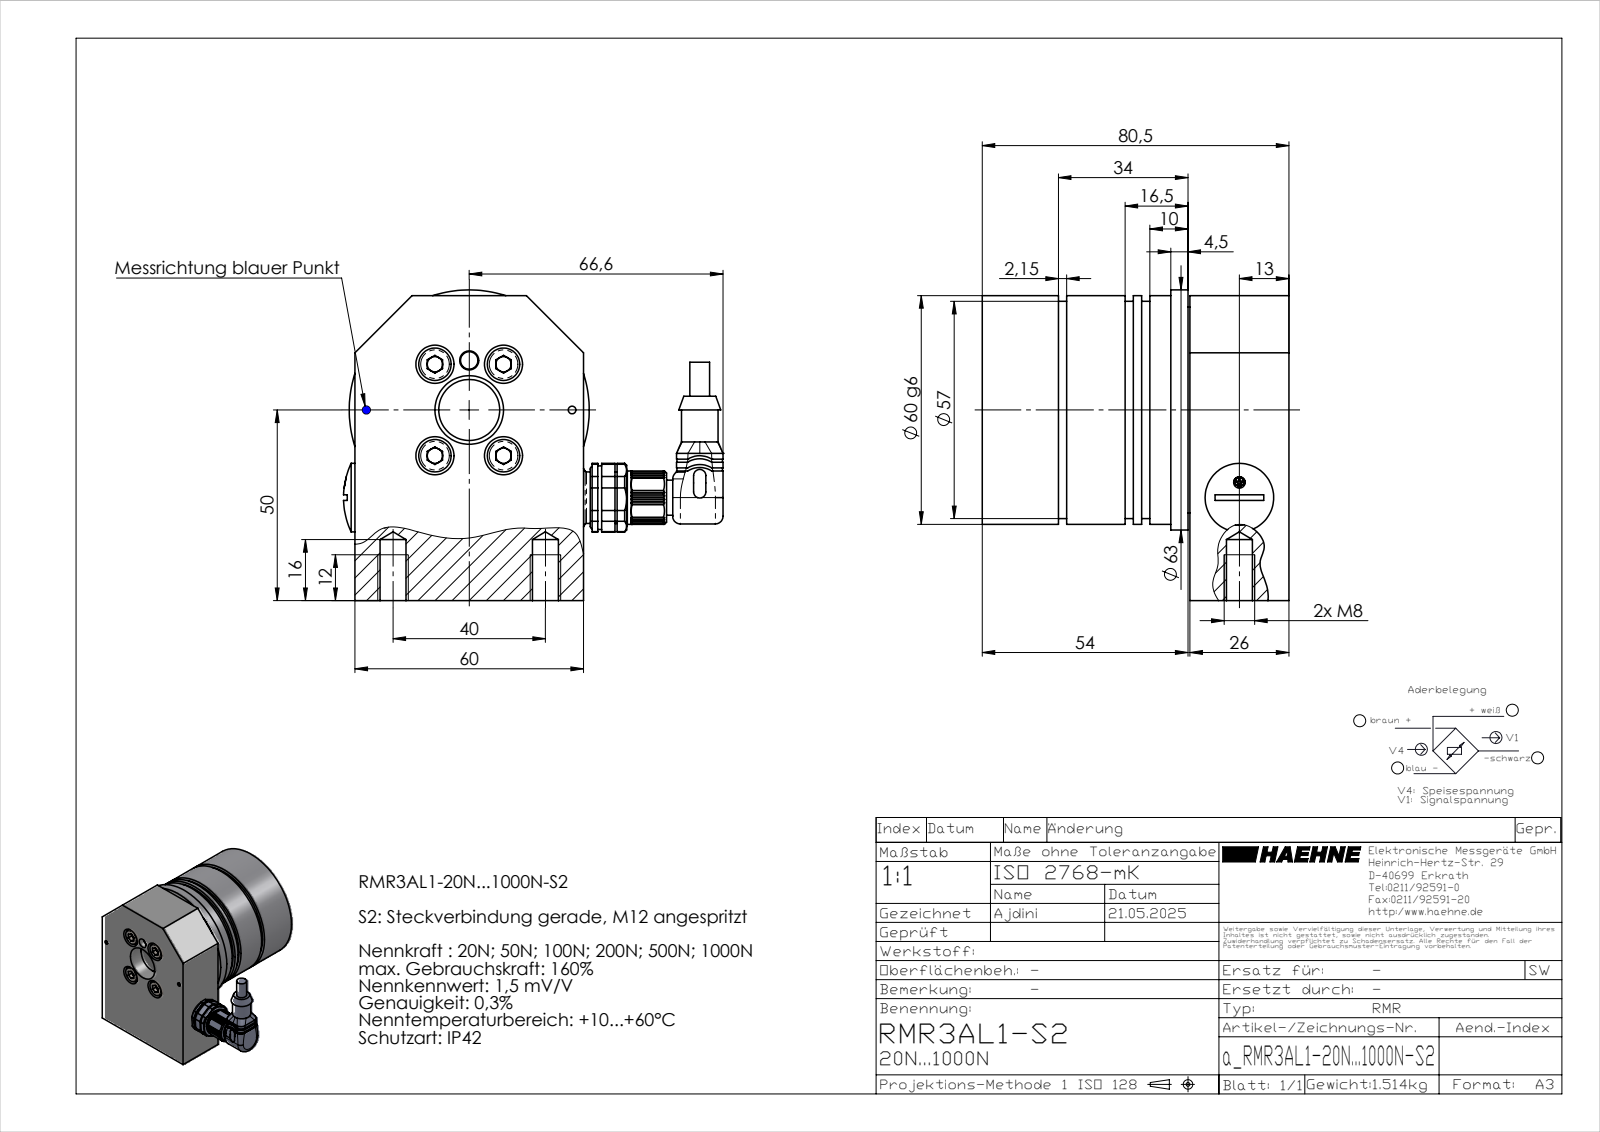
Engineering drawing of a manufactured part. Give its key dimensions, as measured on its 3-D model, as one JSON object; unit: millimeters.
{"part_name": "a_RMR3AL1-20N...1000N-S2", "step_written_by": "SolidWorks 2023 (AUTOMOTIVE_DESIGN)", "units": "millimeters", "bodies": {"solids": 15, "faces": 974, "planar": 533, "cylindrical": 248, "other": 193}, "overall_size": [99.6, 81.5, 80.5], "volume_mm3": 235738, "surface_area_mm2": 73396, "round_holes": [[1.1, 4], [1.15, 4], [1.6, 4], [1.85, 4], [4.2, 4], [5.3, 4], [10, 4], [2, 2], [6.8, 2], [0.64, 1], [1.2, 1], [3, 1]], "round_bosses_or_shafts": [[0.86, 5], [8.5, 4], [5, 4], [1.8, 4], [1.55, 4], [1.5, 4], [1, 4], [63, 1]], "partial_cylinders_radius": [[0.2, 16], [0.3, 9], [0.4, 4], [0.53, 4], [1, 4], [1.27, 4], [6, 4], [1.6, 2]], "face_to_face_distances": [11.5, 48.5, 37, 73, 62, 11, 47, 15, 26, 7.5], "hole_center_spacings": [2.5, 3.54, 15, 21.63, 37.95, 5, 9.06, 18]}
